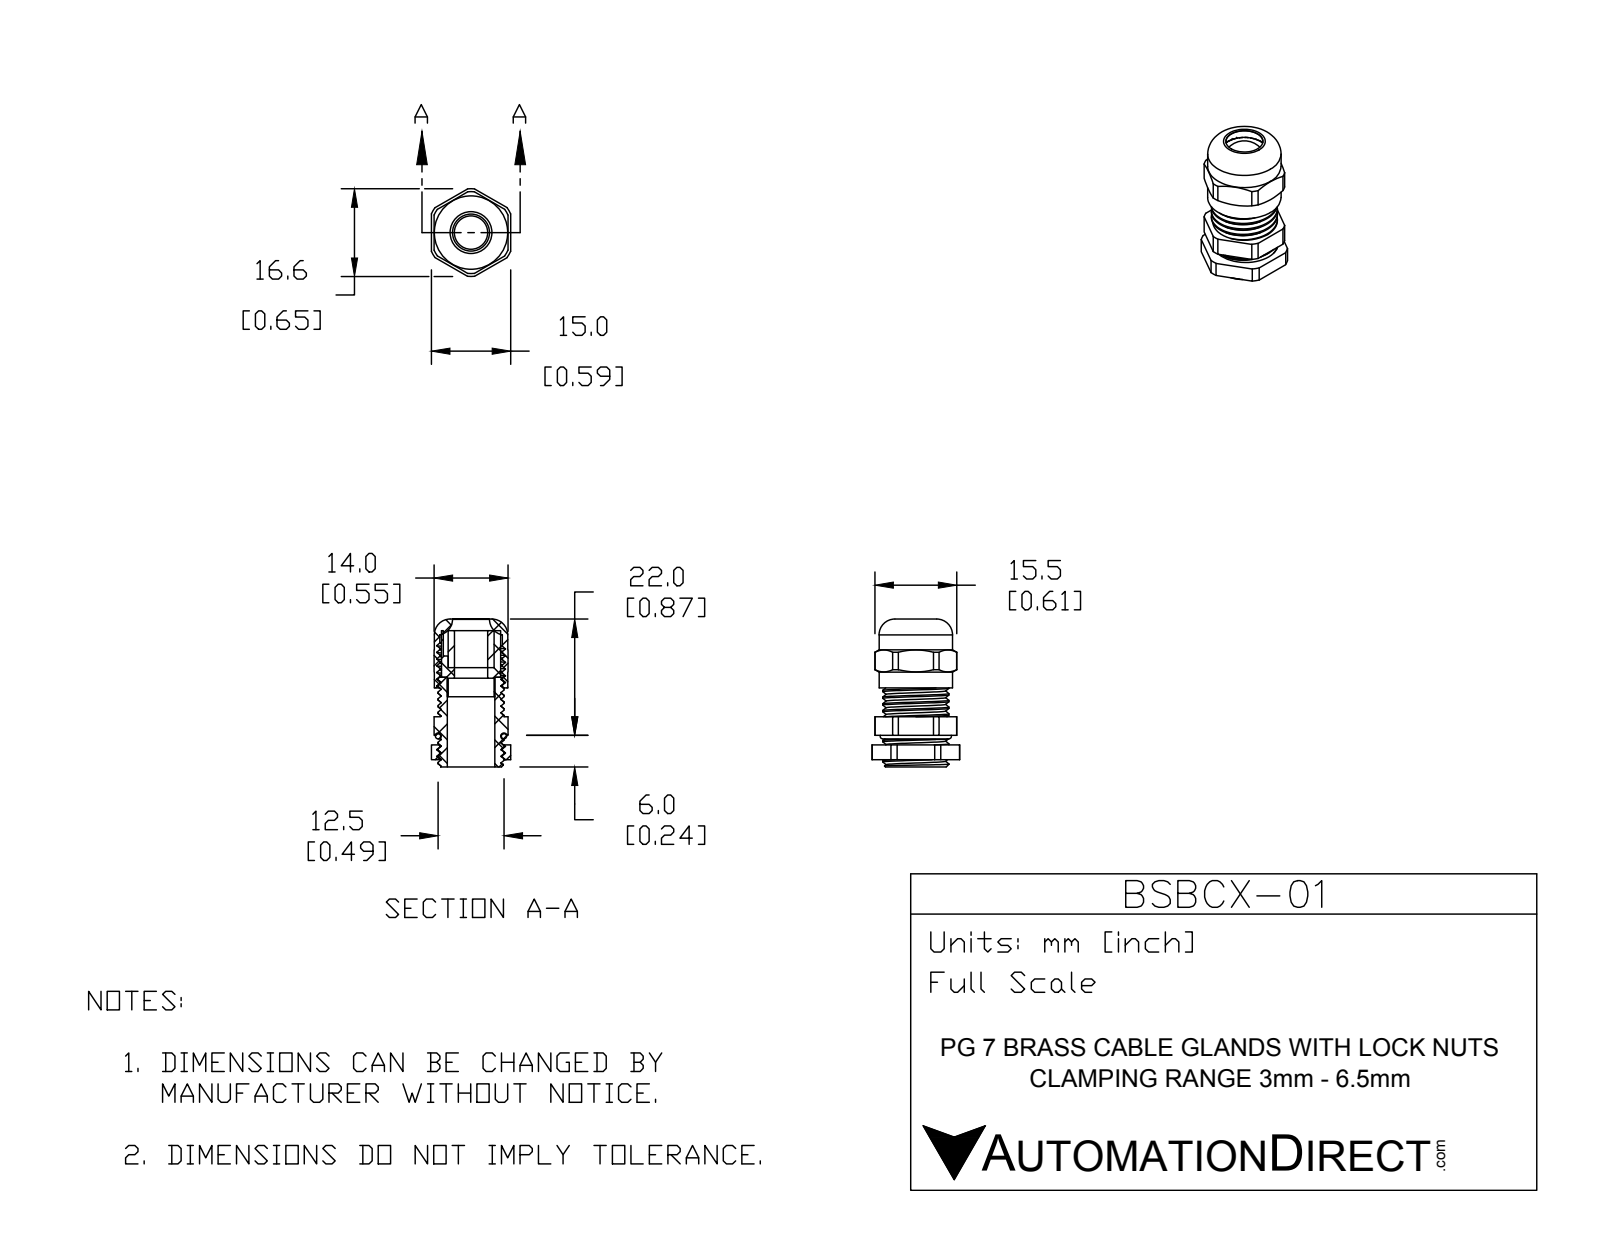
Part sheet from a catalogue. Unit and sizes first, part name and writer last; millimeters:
Units: millimetres
Overall size (bounding box): 28 × 16.6 × 15
Round holes (diameter × count): ⌀6.3 ×1, ⌀7 ×1, ⌀8.7 ×1, ⌀9 ×1, ⌀11.83 ×1
Round bosses / shafts (diameter × count): ⌀13.9 ×1, ⌀12.5 ×1, ⌀11.2 ×1
Partial cylindrical surfaces — rounded edges, fillets, slot ends (radius × count): R7.75 ×1, R8.3 ×1
Main face-to-face distances: 0.5, 14, 14.5, 15, 15.63, 2.8, 12.83, 7, 17.43, 14.63
Volume: 2 415 mm³ · Surface area: 4 959 mm²
Bodies: 6 solids, 250 faces (135 planar, 84 cylindrical, 31 other)
Part name (STEP PRODUCT): BSBCX-01
STEP written by: SolidWorks 2015 (CONFIG_CONTROL_DESIGN)
